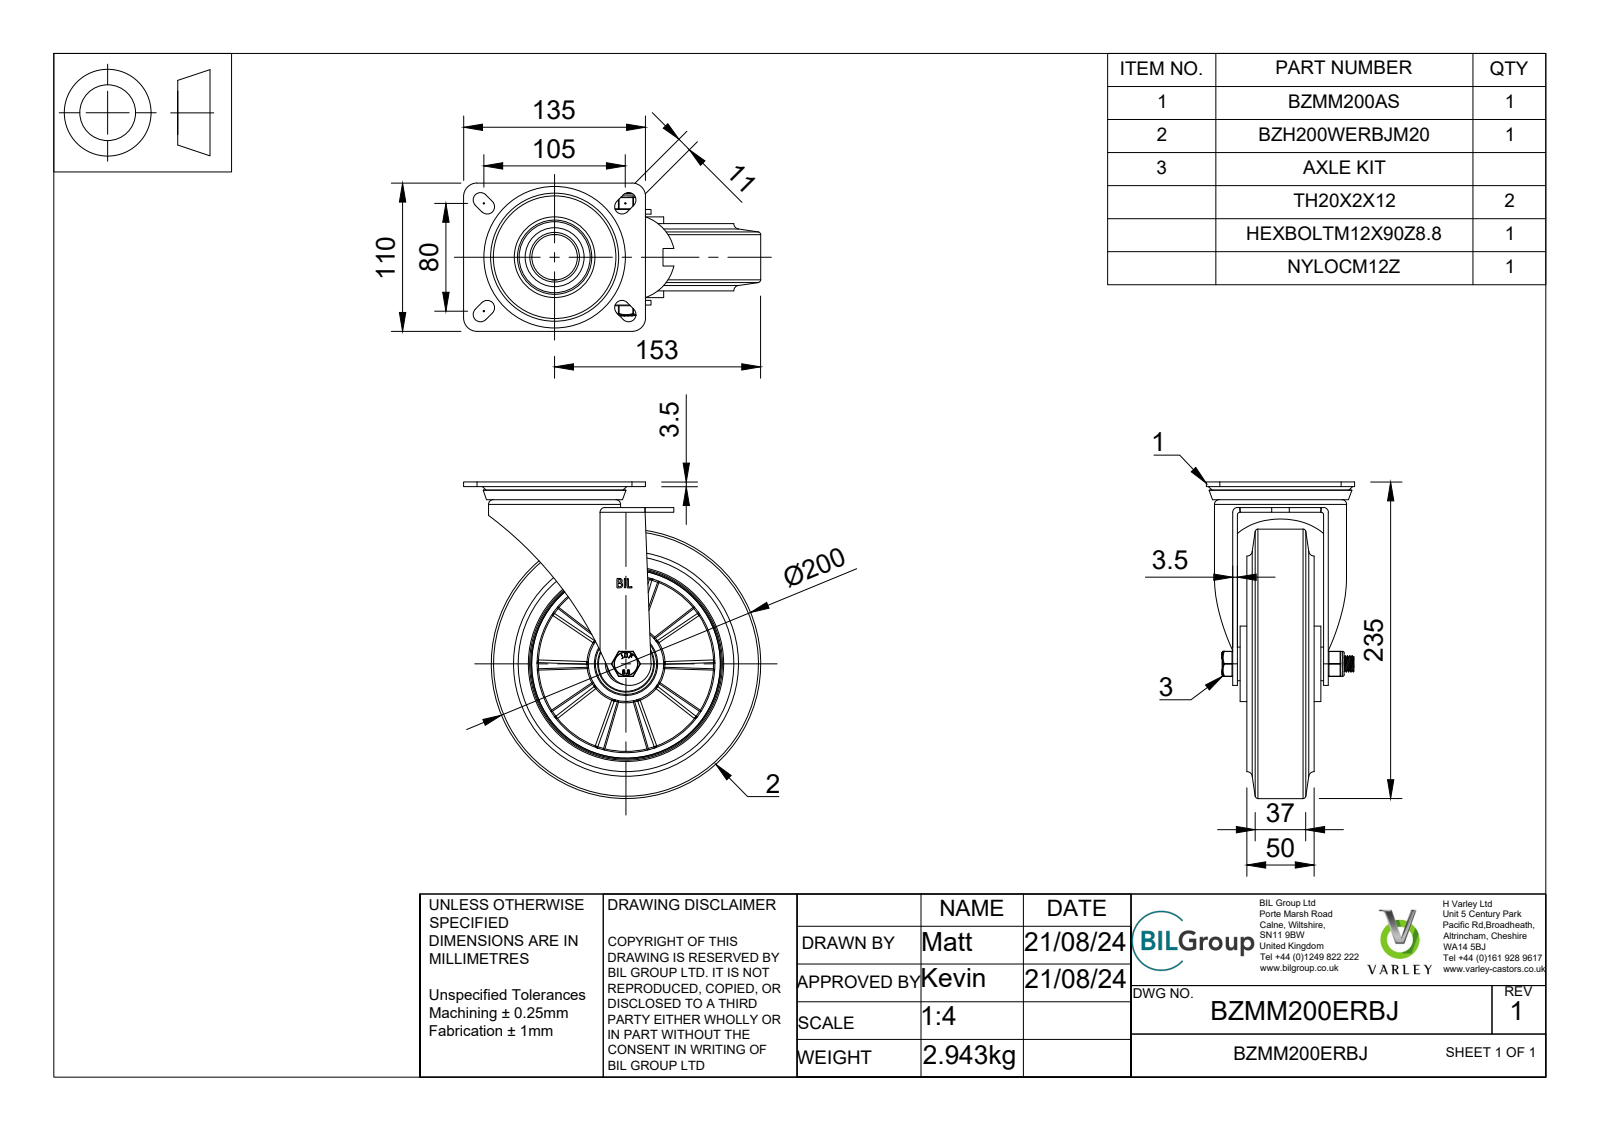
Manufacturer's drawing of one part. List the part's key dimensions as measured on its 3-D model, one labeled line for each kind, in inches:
Part name (STEP PRODUCT): BZMM200ERBJ v3; BZMM200AS - 2 - 64 v1; ZINC PLATED, PRESSED STEEL TOP PLATE; ZINC PLATED, PRESSED STEEL TOP PLATE Geometry (+7 more)
STEP written by: Autodesk Translation Framework v13.14.0.145 (AUTOMOTIVE_DESIGN)
Units: inches
Bodies: 77 solids, 1399 faces (484 planar, 213 cylindrical, 702 other)
Overall size (bounding box): 9.252 × 8.681 × 4.331
Volume: 68.29 in³ · Surface area: 532.1 in²
Round holes (diameter × count): ⌀0.472 ×1, ⌀0.48 ×1, ⌀0.551 ×1, ⌀0.787 ×1, ⌀1.122 ×1, ⌀1.213 ×1, ⌀1.329 ×1, ⌀1.587 ×1, ⌀1.594 ×1, ⌀1.654 ×1, ⌀1.732 ×1, ⌀1.85 ×1
Round bosses / shafts (diameter × count): ⌀7.874 ×1, ⌀5.571 ×1, ⌀3.858 ×1, ⌀3.071 ×1, ⌀2.205 ×1, ⌀1.969 ×1, ⌀1.606 ×1, ⌀1.565 ×1
Partial cylindrical surfaces — rounded edges, fillets, slot ends (radius × count): R0.02 ×19, R0.217 ×8, R0.019 ×4, R0.035 ×4, R0.069 ×4, R0.394 ×4, R0.035 ×2, R0.035 ×2
Main face-to-face distances: 0.276, 0.138, 1.969, 0.551, 0.394, 0.118, 0.689, 1.693, 2.244, 0.354
